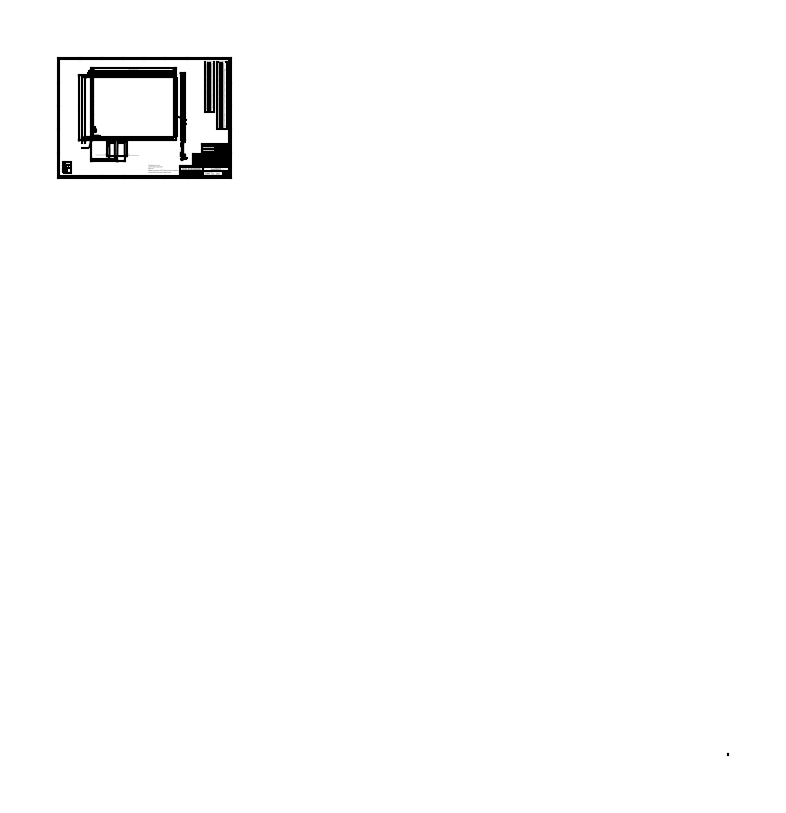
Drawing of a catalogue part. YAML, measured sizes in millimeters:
part_name: "DUS-N150A060B"
step_written_by: "Autodesk Inventor 2020 (AUTOMOTIVE_DESIGN)"
units: millimeters
bodies: {solids: 1, faces: 412, planar: 406, cylindrical: 6, other: 0}
overall_size: [448, 356.04, 2.35]
volume: 185932
surface_area: 166499
partial_cylinders:
  - {radius: 0.2, count: 4}
  - {radius: 5, count: 2}
face_to_face_distances: [2.35, 1.2, 1.15, 1.25, 1.1, 246.7, 320, 0.8, 1.55, 0.4]
